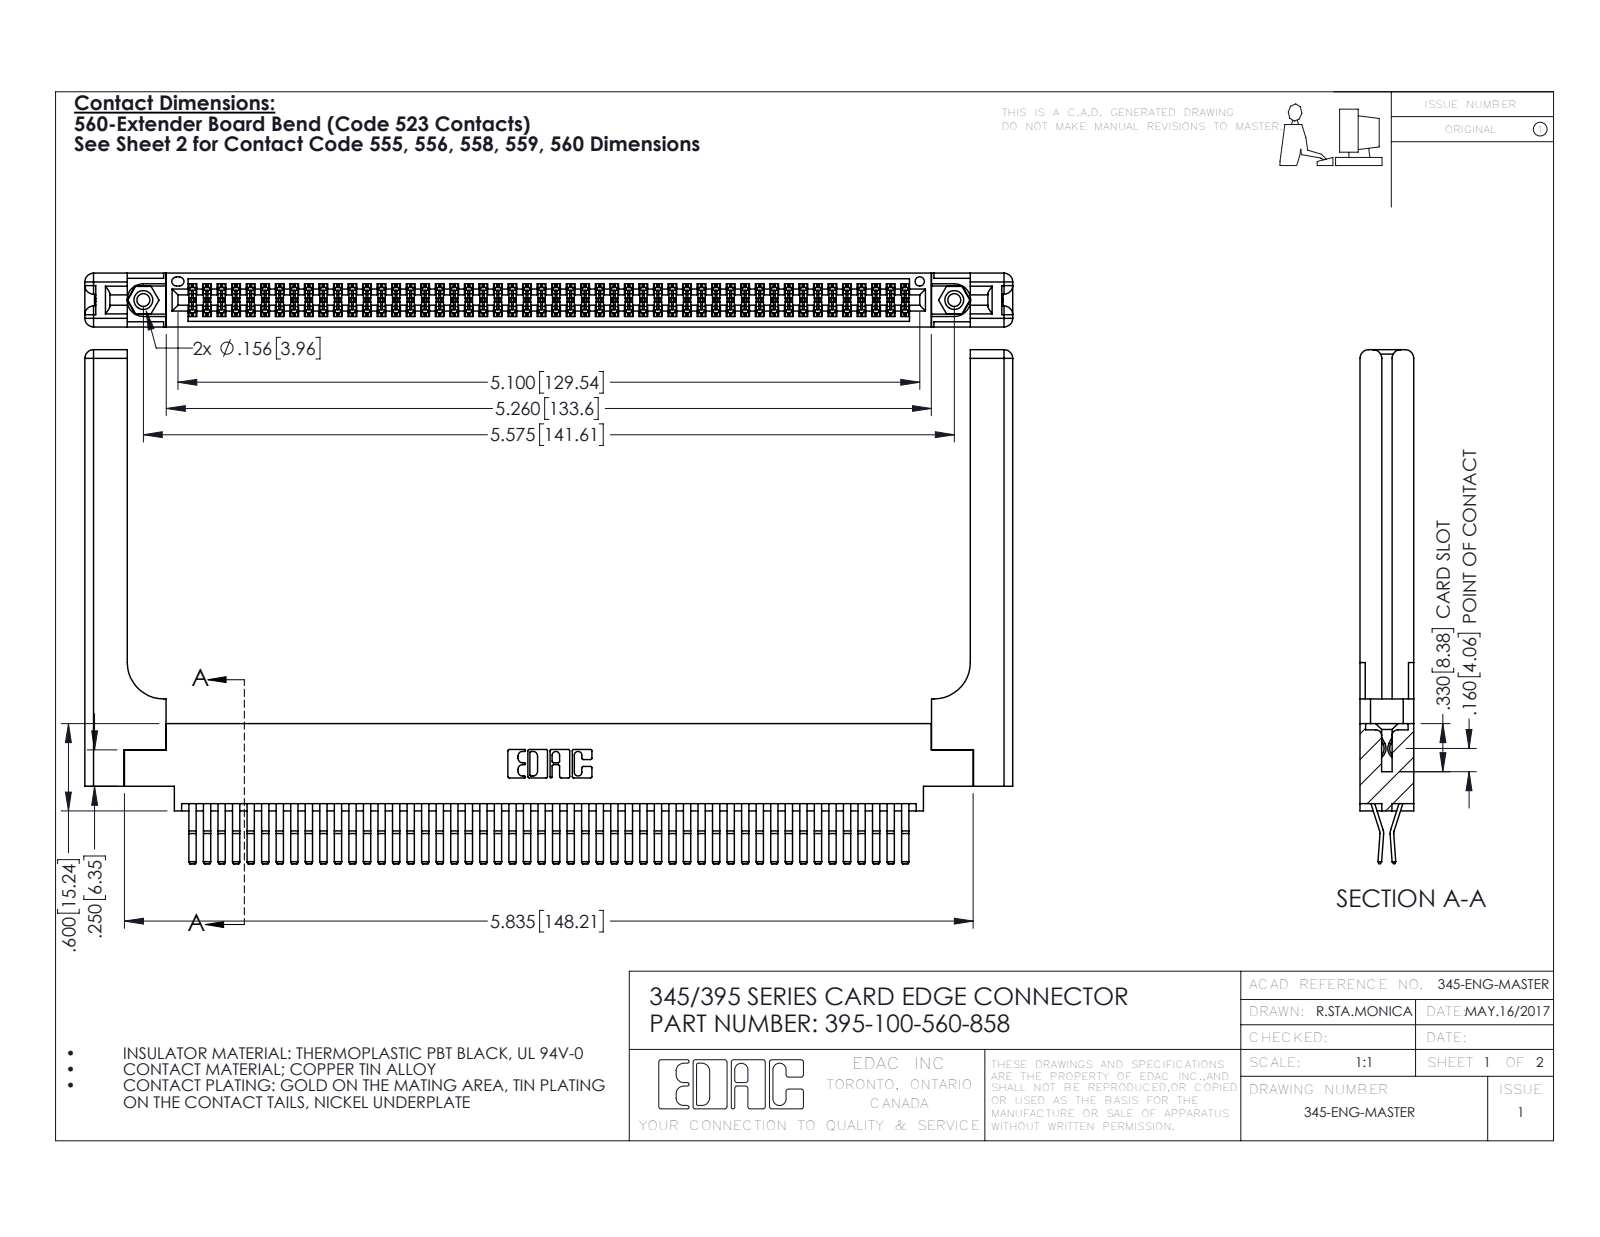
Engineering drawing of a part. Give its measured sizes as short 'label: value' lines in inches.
name: 345-292-001_560 Tail; 345 Part_0.170 Offset - 0.156 Dia-TH; 345-220-058_345-220-058; 395-100-560-858 (+1 more)
written by: SolidWorks 2016 (CONFIG_CONTROL_DESIGN)
unit: in
bodies: 105 solids, 5586 faces (3532 planar, 1994 cylindrical, 60 other)
size: 6.379 × 3.532 × 0.37
volume: 1.515 in³; area: 48.39 in²
holes: 2× ⌀0.089, 2× ⌀0.125, 2× ⌀0.156, 1× ⌀0.064
bosses: 2× ⌀0.155
rounds: 151× R0.006, 22× R0.01, 16× R0.06, 6× R0.007, 6× R0.031, 3× R0.026, 2× R0.01, 2× R0.014
face distances: 0.072, 0.37, 0.298, 0.025, 0.098, 0.272, 0.2, 0.225, 0.148, 0.15
hole spacings: 0.27, 5.339, 5.575
